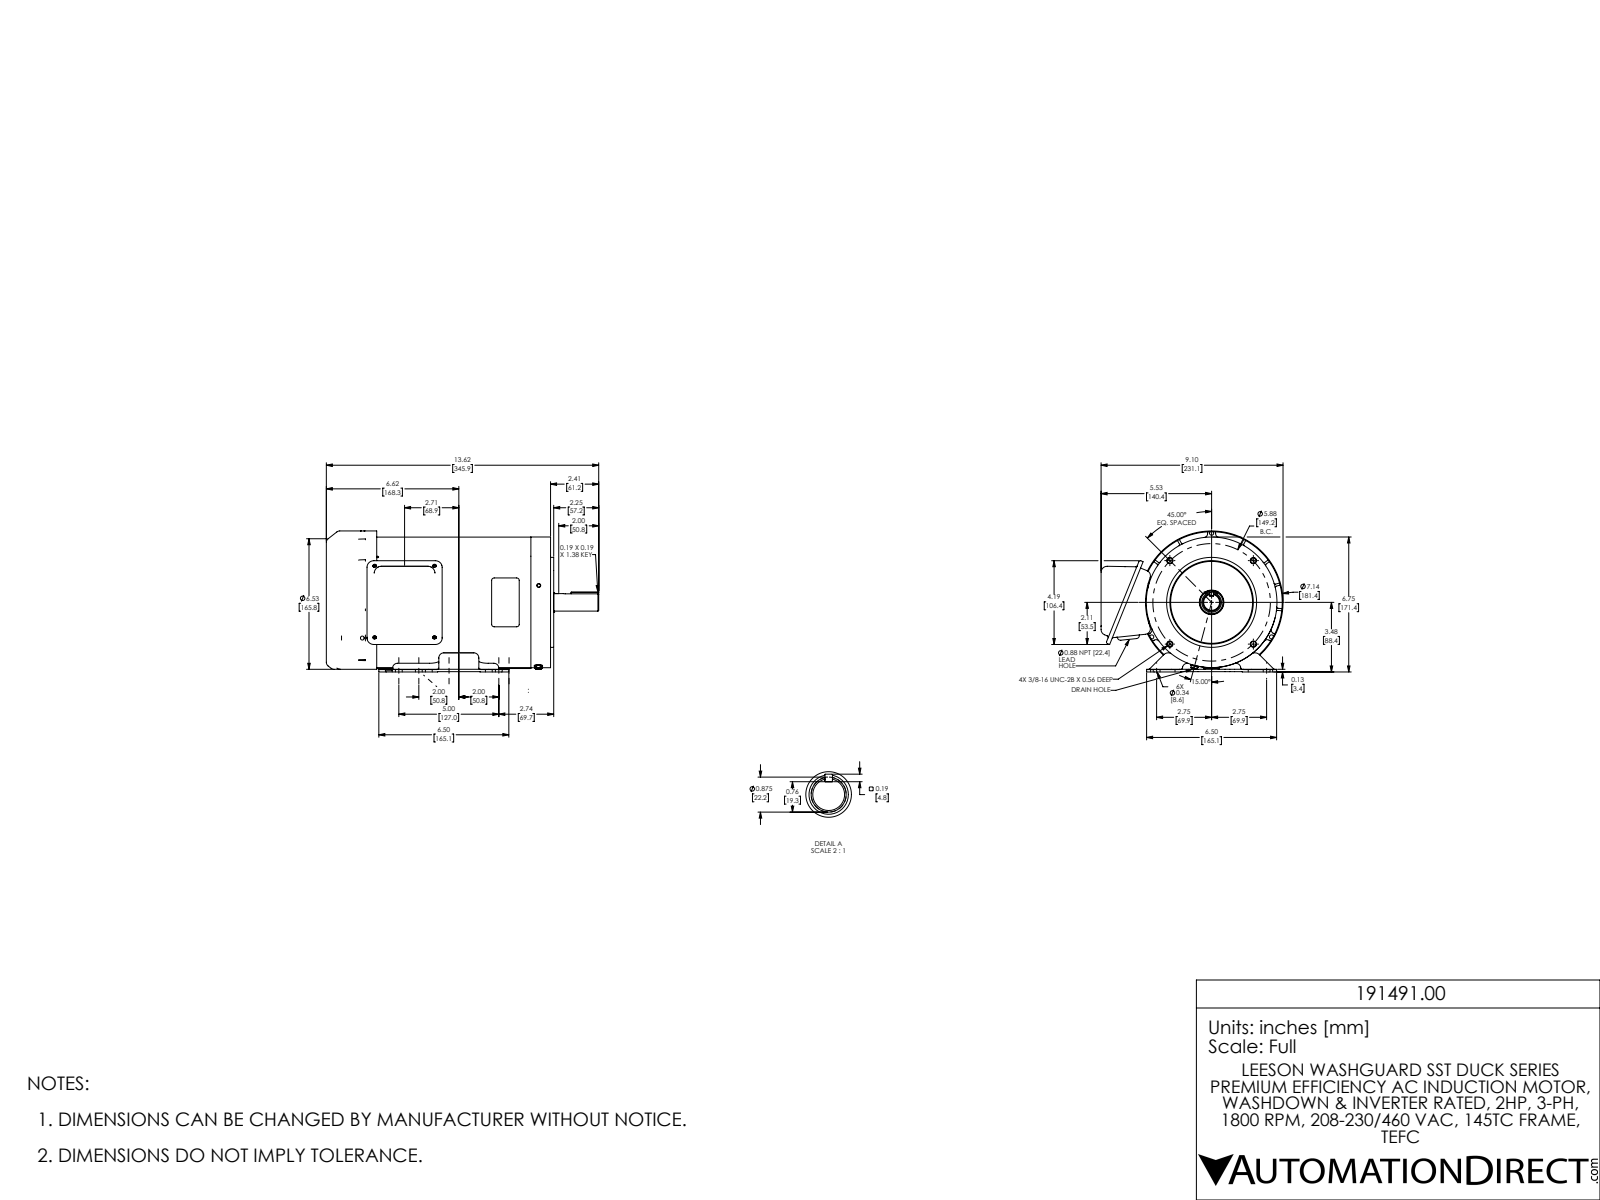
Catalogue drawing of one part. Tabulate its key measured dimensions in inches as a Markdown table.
| quantity | value |
| --- | --- |
| part name | 191487 |
| STEP written by | SolidWorks 2017 (AUTOMOTIVE_DESIGN) |
| units | inches |
| bodies | 18 solids, 3071 faces (553 planar, 844 cylindrical, 1674 other) |
| overall size | 13.62 × 9.098 × 7.051 |
| volume | 106.1 in³ |
| surface area | 1 140 in² |
| round holes (diameter × count) | 0.147 × 13, 0.197 × 11, 0.138 × 9, 0.165 × 8, 0.13 × 6, 0.34 × 6, 0.177 × 4, 0.268 × 4, 0.271 × 4, 0.21 × 3, 0.103 × 2, 0.136 × 2 |
| round bosses / shafts (diameter × count) | 0.348 × 3, 0.164 × 3, 7.142 × 1, 6.535 × 1, 6.525 × 1, 6.409 × 1, 6.133 × 1, 4.5 × 1 |
| partial cylindrical surfaces (radius × count) | 0.03 × 122, 0.094 × 81, 0.06 × 38, 0.079 × 28, 0.276 × 13, 0.17 × 12, 0.25 × 10, 0.236 × 9 |
| main face-to-face distances | 0.039, 0.118, 9.587, 9.547, 10.976, 0.015, 0.197, 0.119, 11.212, 11.172 |
| hole center spacings | 3.858, 2.953, 4.088, 0.236, 2.227, 2.27, 2.992, 3.858 |
